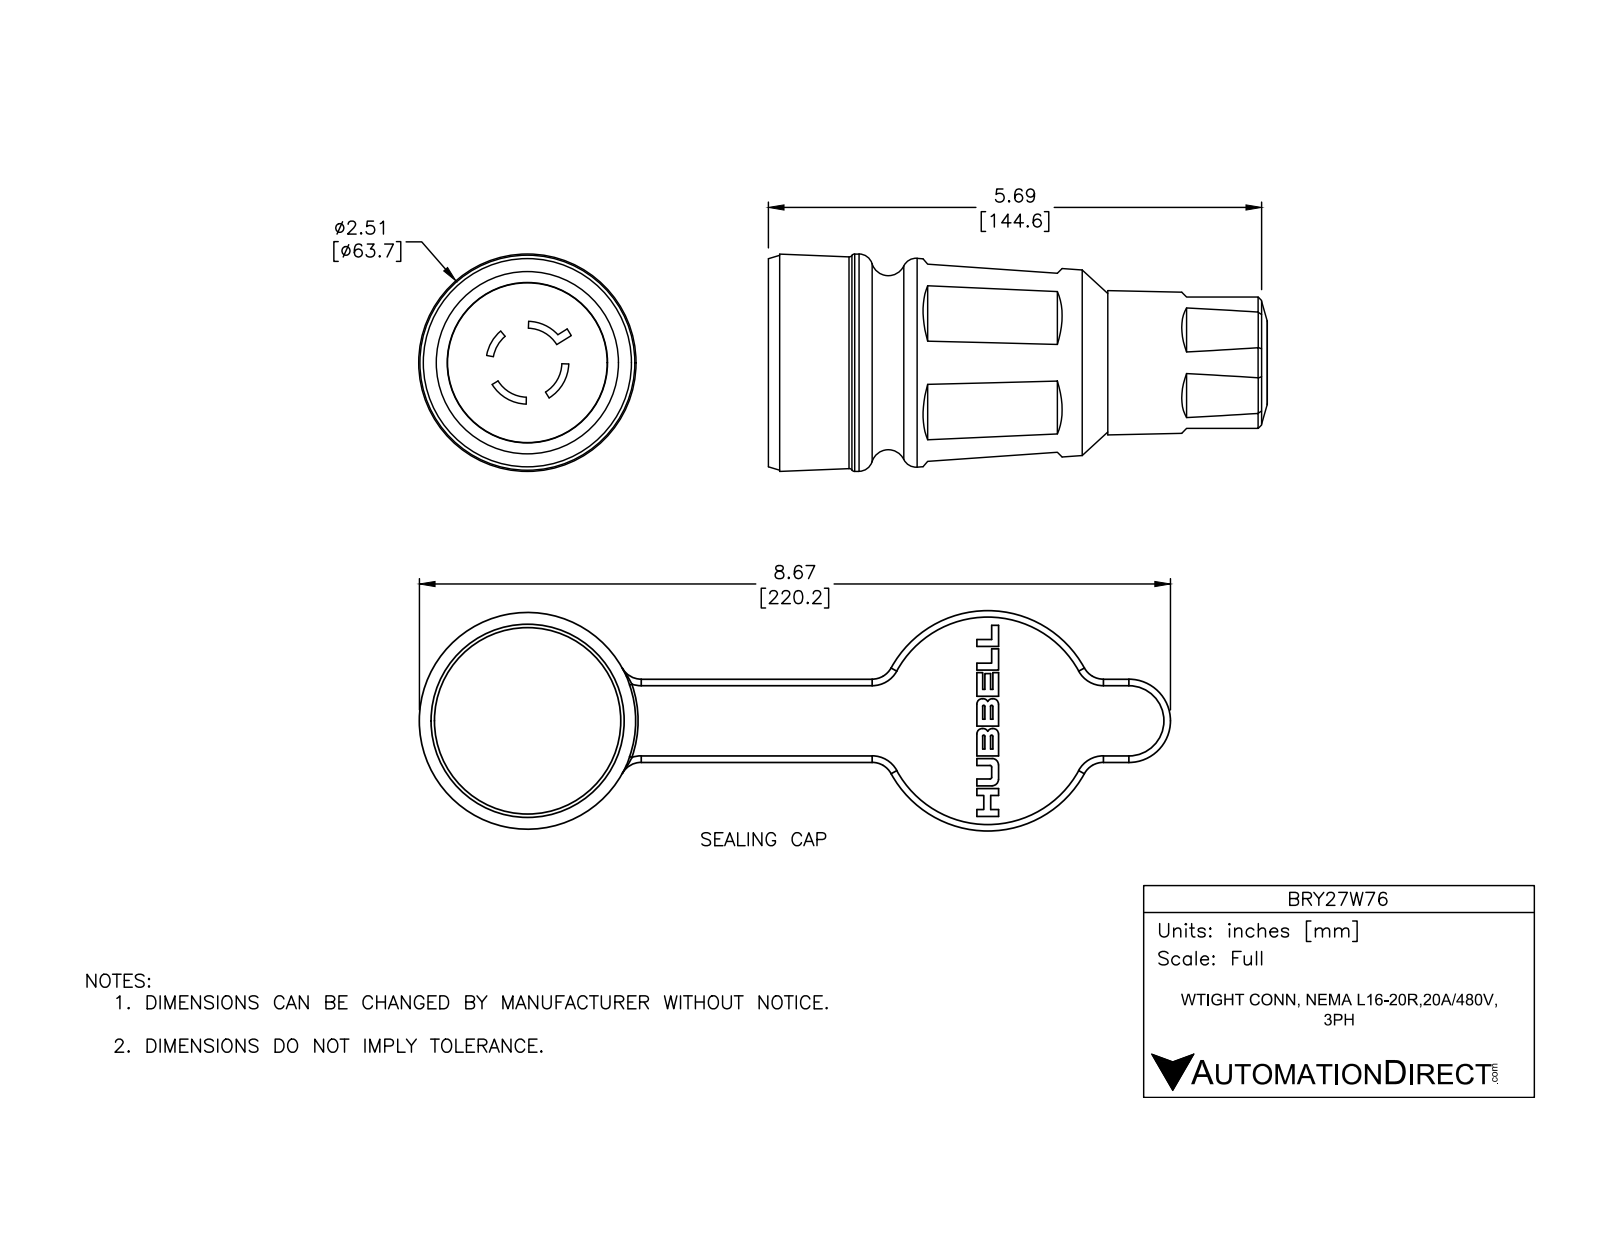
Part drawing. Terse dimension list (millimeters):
name: BRY27W76; BRY27W-CAP; BRY27W76-CONNECTOR
written by: SolidWorks 2016 (AUTOMOTIVE_DESIGN)
unit: mm
bodies: 5 solids, 186 faces (71 planar, 53 cylindrical, 62 other)
size: 218.6 × 146.3 × 64
volume: 299 400 mm³; area: 80 710 mm²
holes: 1× ⌀22, 1× ⌀36, 1× ⌀45, 1× ⌀47, 1× ⌀53, 1× ⌀53.4
bosses: 1× ⌀64, 1× ⌀63.7, 1× ⌀61.6, 1× ⌀56, 1× ⌀51.7, 1× ⌀46.8, 1× ⌀31.5
rounds: 4× R1.8, 4× R6, 2× R4, 1× R10.1, 1× R12.1, 1× R12.2
face distances: 3.7, 12.8, 16.5, 34.4, 21.6, 17.9, 19.8, 7, 3.3, 14.6
hole spacings: 132.8
